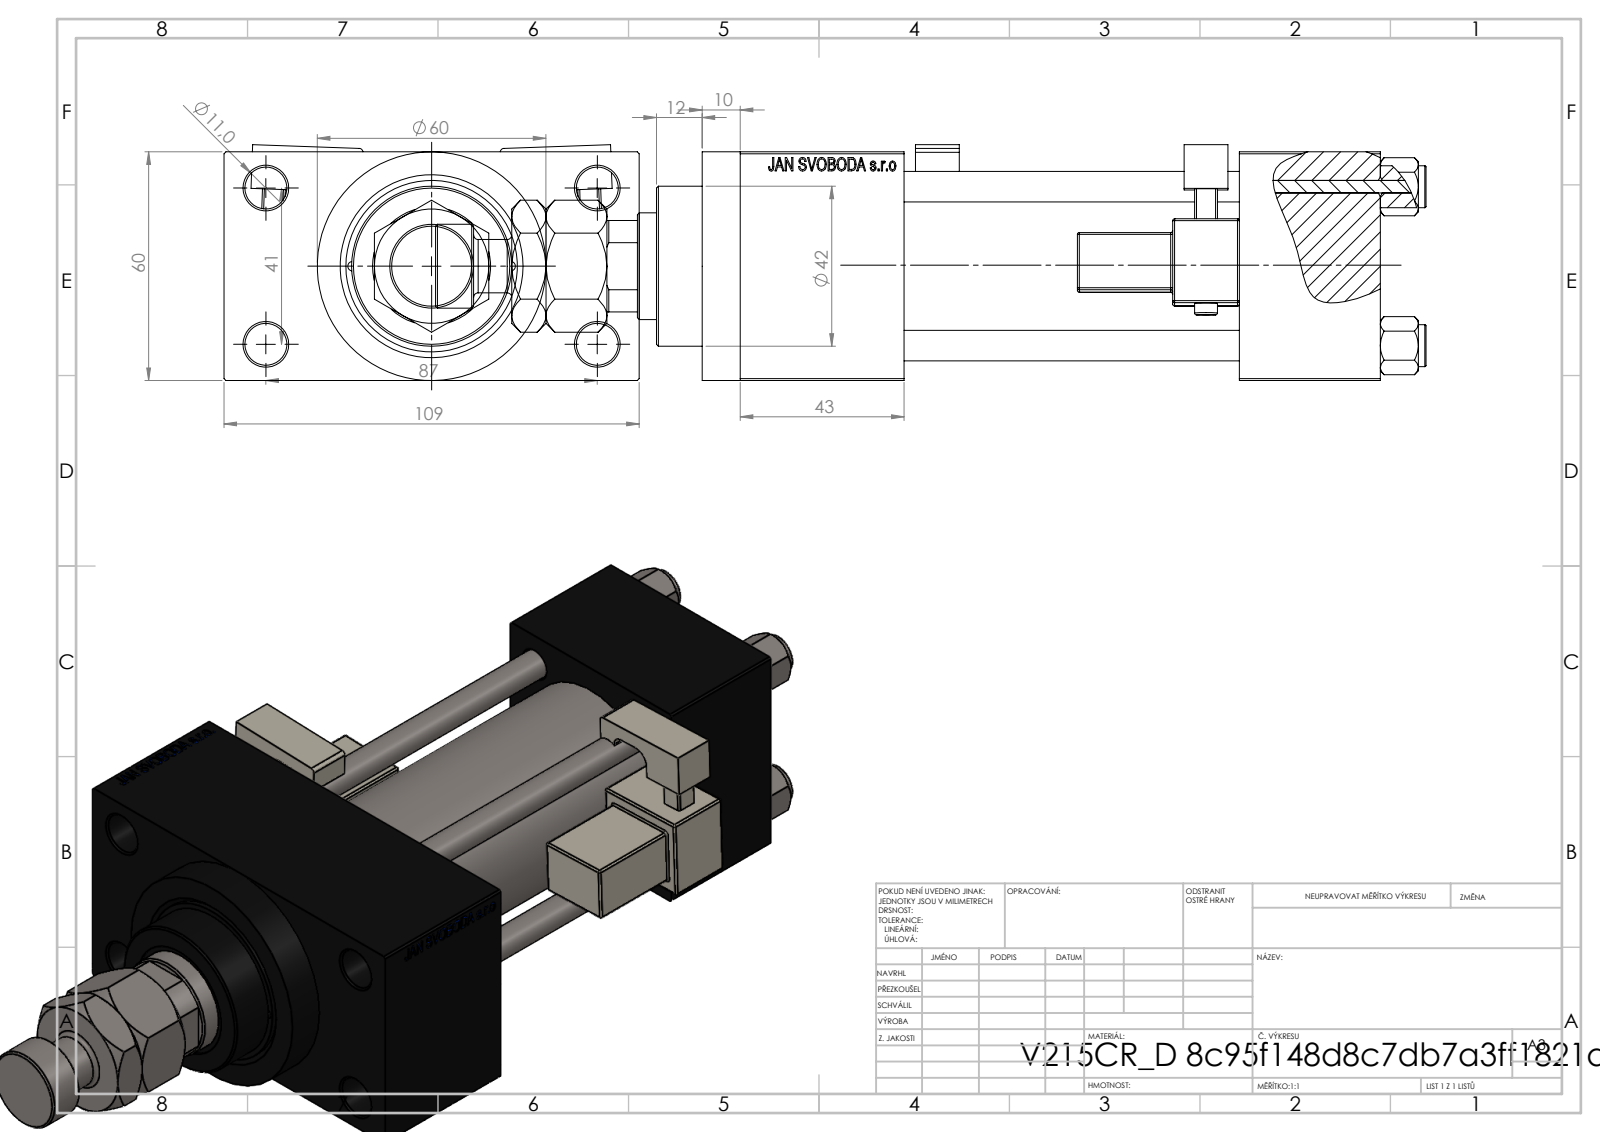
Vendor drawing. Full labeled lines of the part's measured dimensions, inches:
Part name (STEP PRODUCT): MFA; V215_VC_A; V215CR_MSU; V215CR_VCP_D (+3 more)
STEP written by: SolidWorks 2019 (CONFIG_CONTROL_DESIGN)
Units: inches
Bodies: 14 solids, 1320 faces (576 planar, 156 cylindrical, 588 other)
Overall size (bounding box): 10.236 × 4.291 × 2.437
Volume: 38.49 in³ · Surface area: 248.8 in²
Round holes (diameter × count): ⌀0.315 ×4, ⌀0.433 ×4, ⌀0.098 ×2, ⌀0.276 ×2, ⌀0.656 ×2, ⌀0.945 ×2, ⌀0.728 ×1, ⌀1.102 ×1, ⌀1.22 ×1, ⌀1.575 ×1, ⌀1.772 ×1
Round bosses / shafts (diameter × count): ⌀0.433 ×4, ⌀0.236 ×2, ⌀2.362 ×1, ⌀1.811 ×1, ⌀1.654 ×1, ⌀0.866 ×1, ⌀0.551 ×1
Partial cylindrical surfaces — rounded edges, fillets, slot ends (radius × count): R0.02 ×48, R0.039 ×2, R0.098 ×2, R0.157 ×2, R0.531 ×1
Main face-to-face distances: 2.362, 3.465, 0.965, 3.327, 1.457, 4.921, 6.614, 5.157, 1.693, 4.291
Hole centre spacings: 0.821, 0.892, 1.161, 1.206, 1.642, 1.832, 1.856, 1.893
